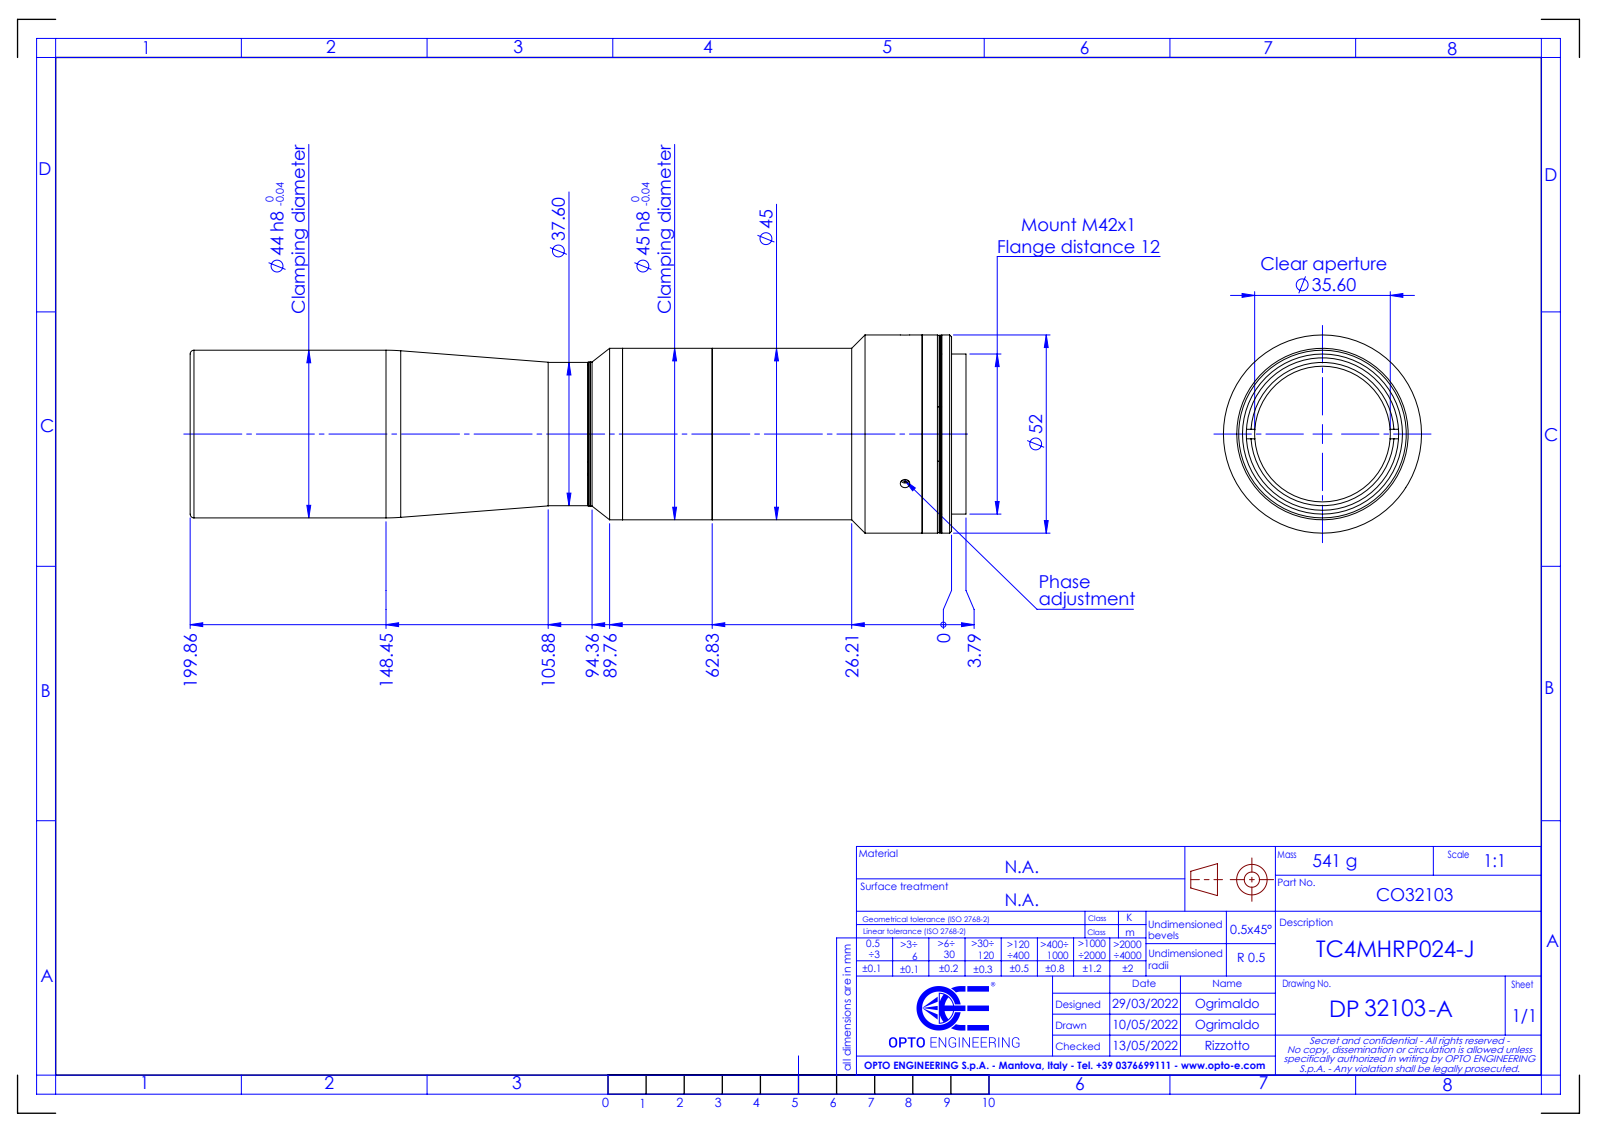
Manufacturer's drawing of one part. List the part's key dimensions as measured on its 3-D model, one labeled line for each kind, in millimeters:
Part name (STEP PRODUCT): DP32103-A_TC4MHRP024-J
STEP written by: SolidWorks 2021 (CONFIG_CONTROL_DESIGN)
Units: millimetres
Bodies: 0 solids, 98 faces (34 planar, 44 cylindrical, 20 other)
Overall size (bounding box): 203.66 × 52 × 52
Round holes (diameter × count): ⌀2.5 ×3, ⌀35.6 ×1, ⌀38 ×1, ⌀40 ×1, ⌀41 ×1
Round bosses / shafts (diameter × count): ⌀52 ×1, ⌀51.8 ×1, ⌀45 ×1, ⌀44 ×1, ⌀42 ×1, ⌀37.8 ×1, ⌀37.6 ×1
Main face-to-face distances: 87.16, 92.3, 5.14, 91.16, 4, 1.14, 94.86, 7.7, 3.7, 2.56
